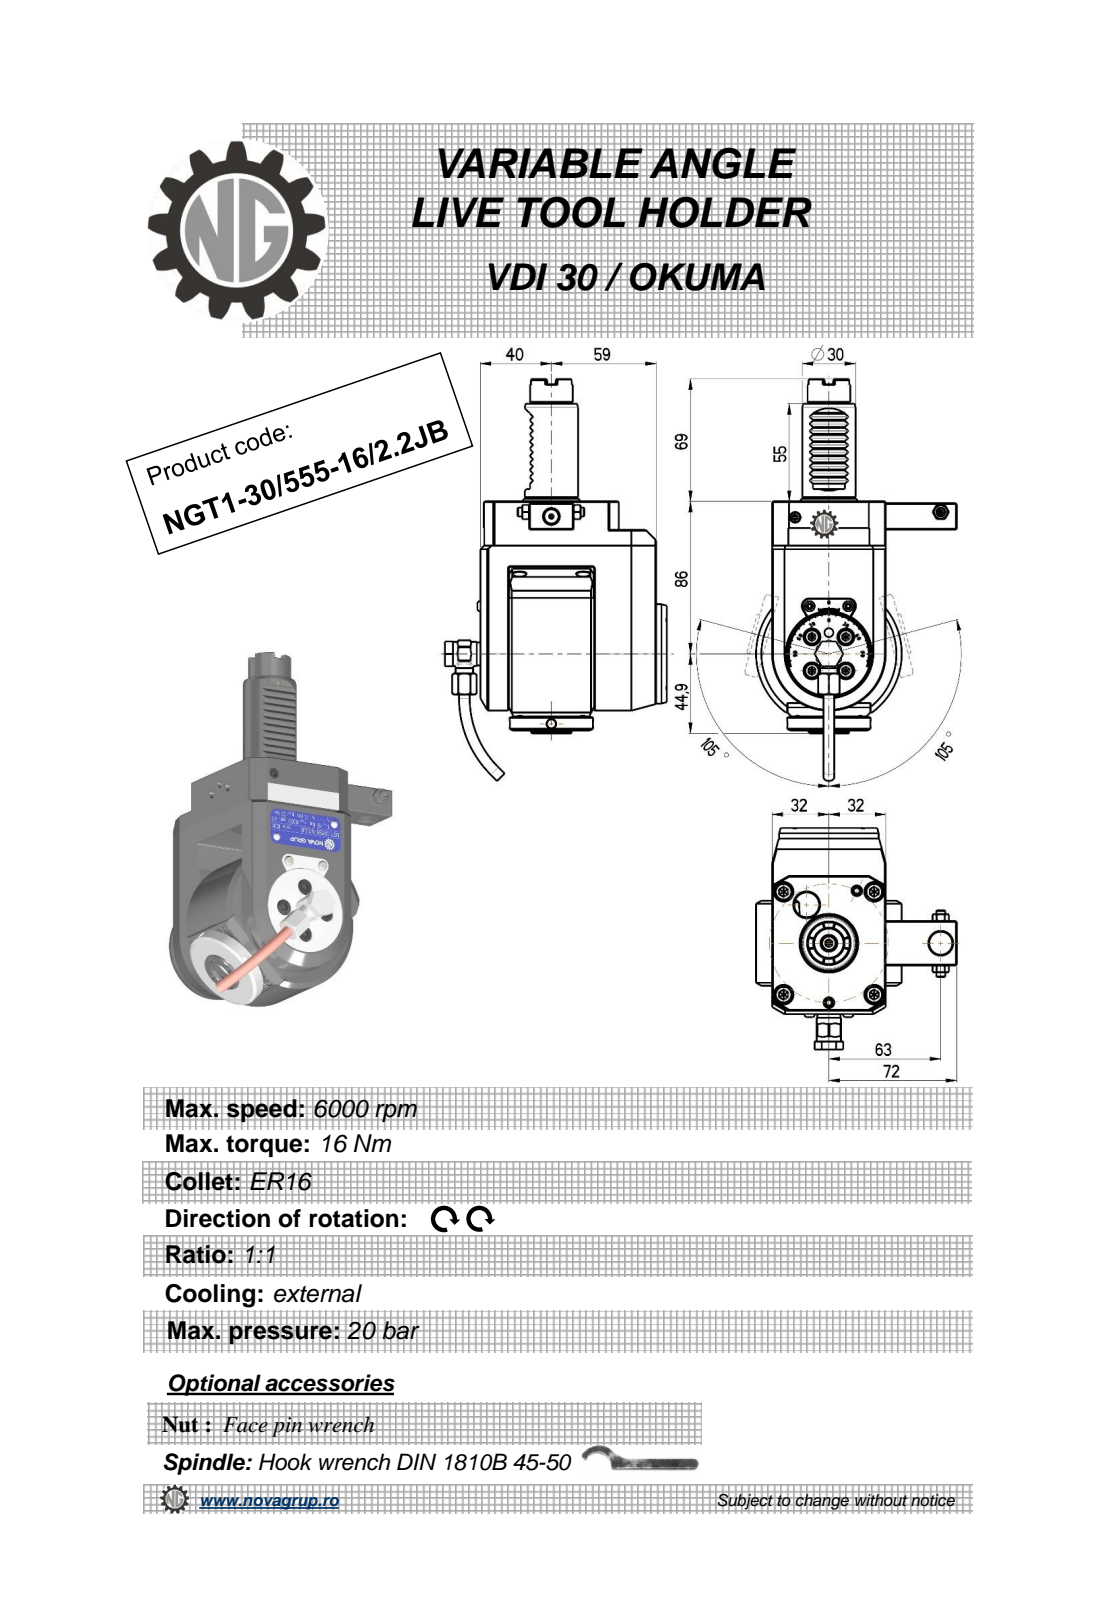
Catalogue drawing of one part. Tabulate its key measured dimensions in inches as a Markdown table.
| quantity | value |
| --- | --- |
| part name | NGT1_30_555_16_2_2JB |
| STEP written by | PRO/ENGINEER BY PARAMETRIC TECHNOLOGY CORPORATION, 2010280 (CONFIG_CONTROL_DESIGN) |
| units | inches |
| bodies | 1 solid, 559 faces (237 planar, 142 cylindrical, 180 other) |
| overall size | 8.924 × 4.917 × 4.449 |
| volume | 48.04 in³ |
| surface area | 115.9 in² |
| round holes (diameter × count) | 0.126 × 4, 0.157 × 3, 0.197 × 2, 0.118 × 1, 0.165 × 1, 0.244 × 1, 0.354 × 1, 0.374 × 1, 0.433 × 1, 0.492 × 1, 0.512 × 1, 0.669 × 1 |
| round bosses / shafts (diameter × count) | 0.394 × 2, 0.236 × 2, 0.224 × 2, 2.205 × 1, 1.85 × 1, 1.417 × 1, 1.181 × 1, 0.945 × 1 |
| partial cylindrical surfaces (radius × count) | 0.01 × 12, 0.012 × 10, 0.006 × 6, 0.02 × 4, 0.039 × 2, 0.303 × 1, 1.26 × 1, 1.614 × 1 |
| main face-to-face distances | 2.52, 0.63, 1.457, 0.827, 3.898, 0.236, 4.134, 0.551, 2.441, 1.378 |
| hole center spacings | 0.364, 0.515, 0.728, 1.963, 1.979, 2.507, 0.016, 1.553 |
